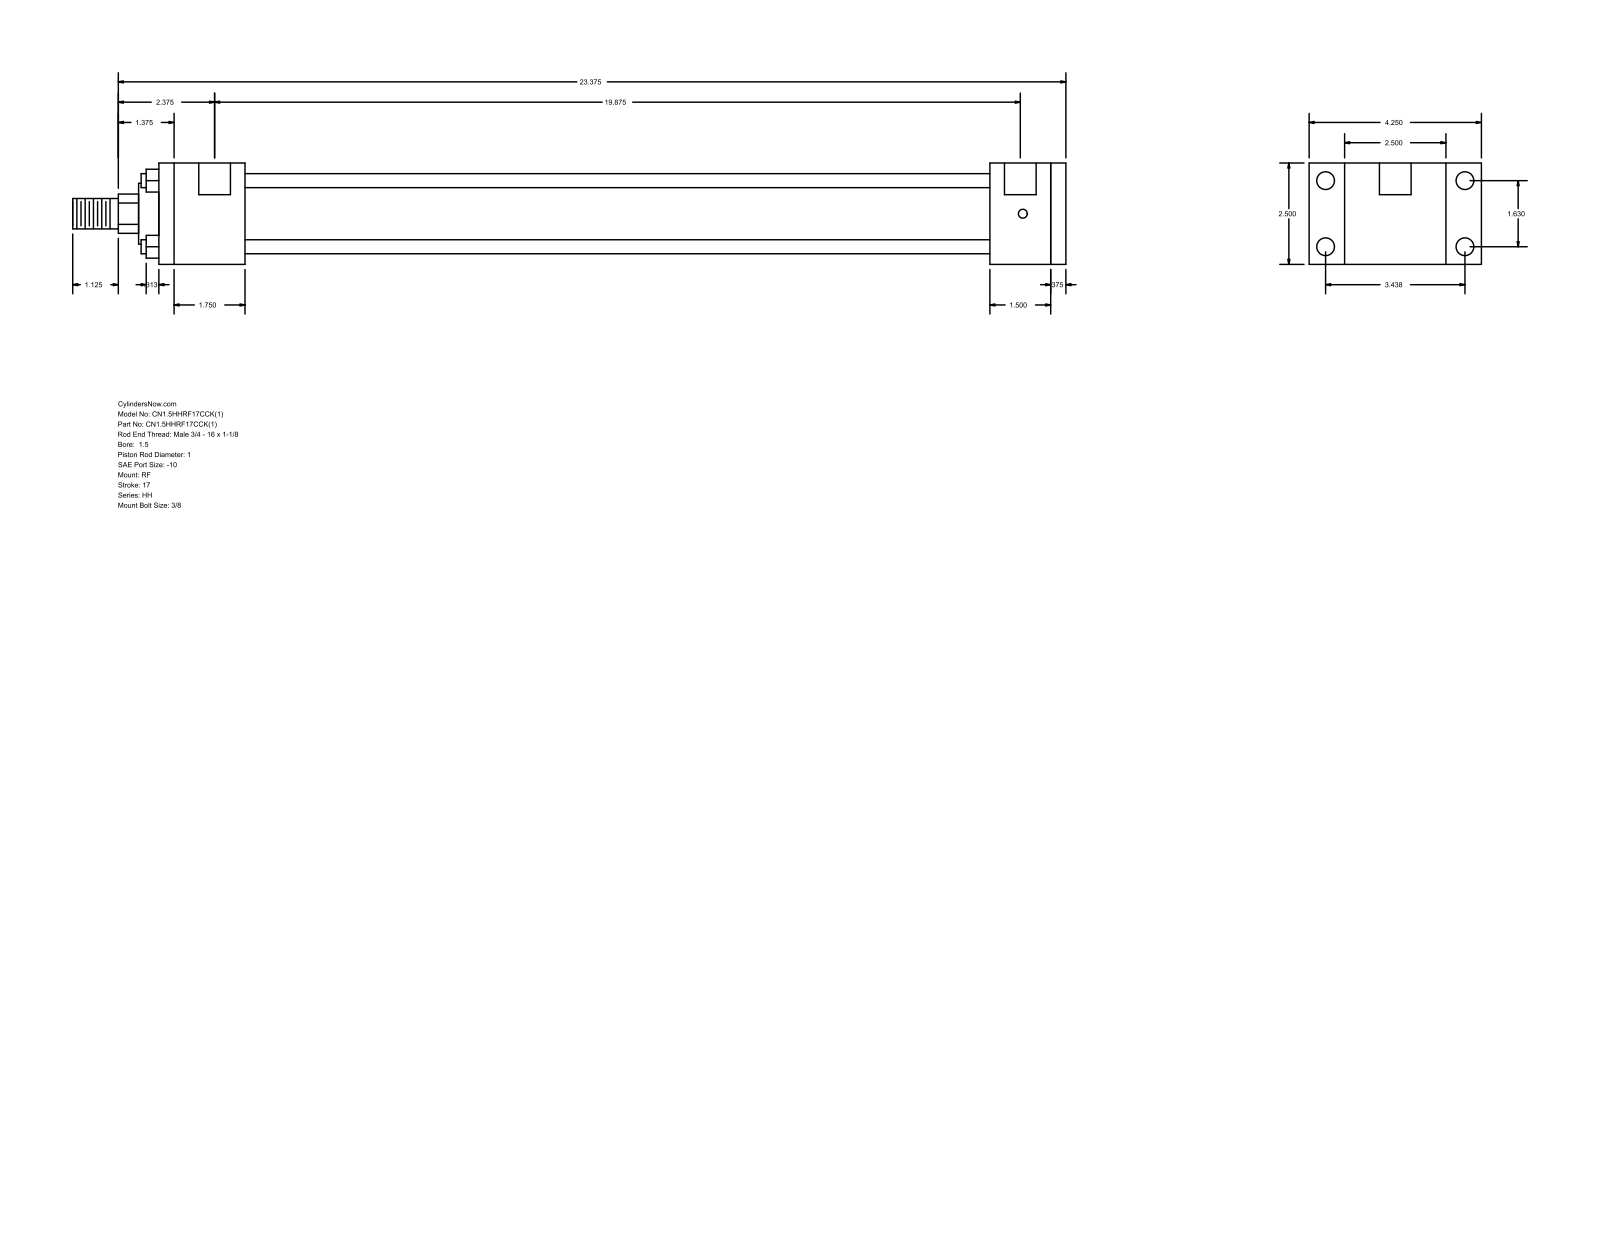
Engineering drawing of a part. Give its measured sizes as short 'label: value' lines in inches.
name: HH_RF__0150_1
written by: GSSL Pune (CONFIG_CONTROL_DESIGN)
unit: in
bodies: 0 solids, 92 faces (64 planar, 28 cylindrical, 0 other)
size: 24.5 × 4.25 × 2.5
holes: 4× ⌀0.219, 4× ⌀0.438, 2× ⌀0.781
bosses: 4× ⌀0.345, 1× ⌀1.75, 1× ⌀1.5, 1× ⌀1, 1× ⌀0.75
rounds: 1× R0.484
face distances: 2.5, 0.375, 1.5, 18.375, 19.875, 20.25, 1.875, 2.125, 20.5, 22
hole spacings: 0.063, 1.63, 3.438, 3.805, 19.937, 20, 19.875
